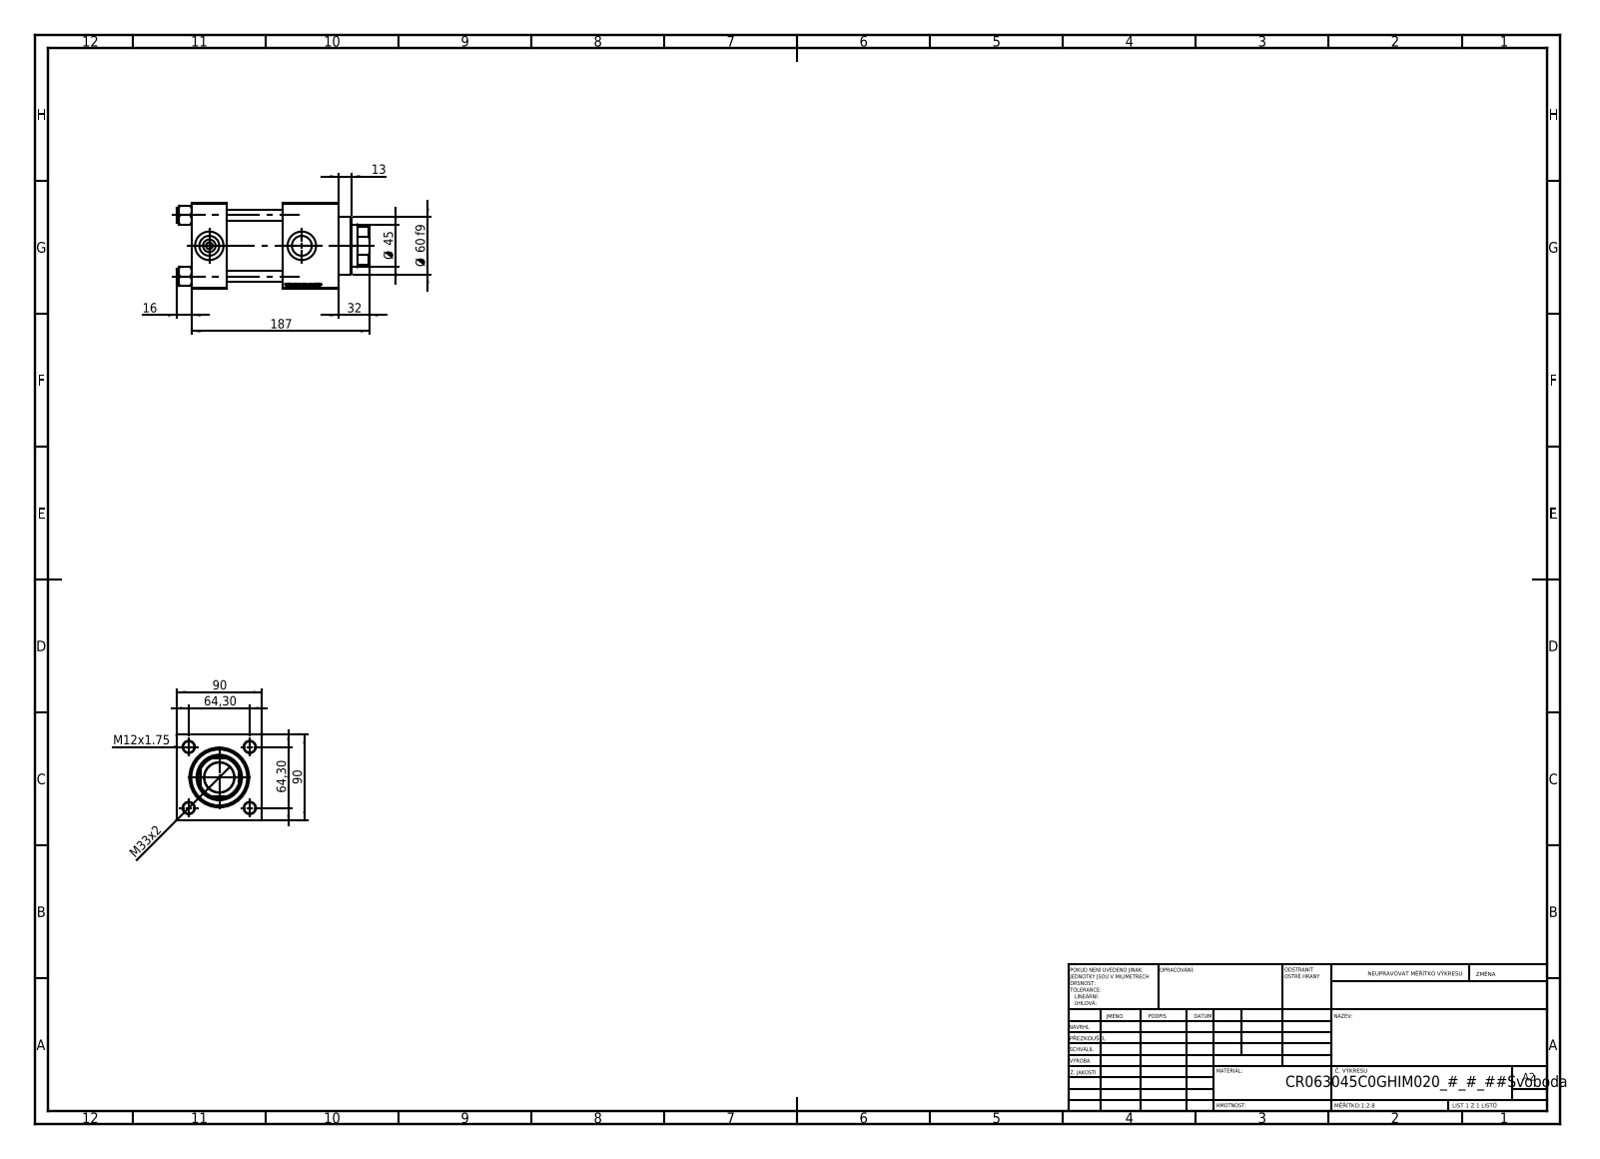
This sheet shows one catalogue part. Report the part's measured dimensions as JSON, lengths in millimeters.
{"part_name": "V215_VC_A; NUT_M5_C; V215CR_C_TYCINKA; V215CR_C_Body (+1 more)", "step_written_by": "SolidWorks 2019 (CONFIG_CONTROL_DESIGN)", "units": "millimeters", "bodies": {"solids": 11, "faces": 1145, "planar": 525, "cylindrical": 84, "other": 536}, "overall_size": [203, 90, 90], "volume_mm3": 997965, "surface_area_mm2": 189930, "round_holes": [[12, 4], [7, 2], [20.96, 2], [30, 2], [31.5, 1], [45, 1], [48, 1], [50, 1], [60, 1], [63, 1]], "round_bosses_or_shafts": [[15, 4], [69, 1]], "partial_cylinders_radius": [[22, 1]], "face_to_face_distances": [90, 59, 37, 96, 155, 118, 126.3, 89.3, 30.3, 28.7], "hole_center_spacings": [45.47, 64.3, 90.93, 97.5]}
